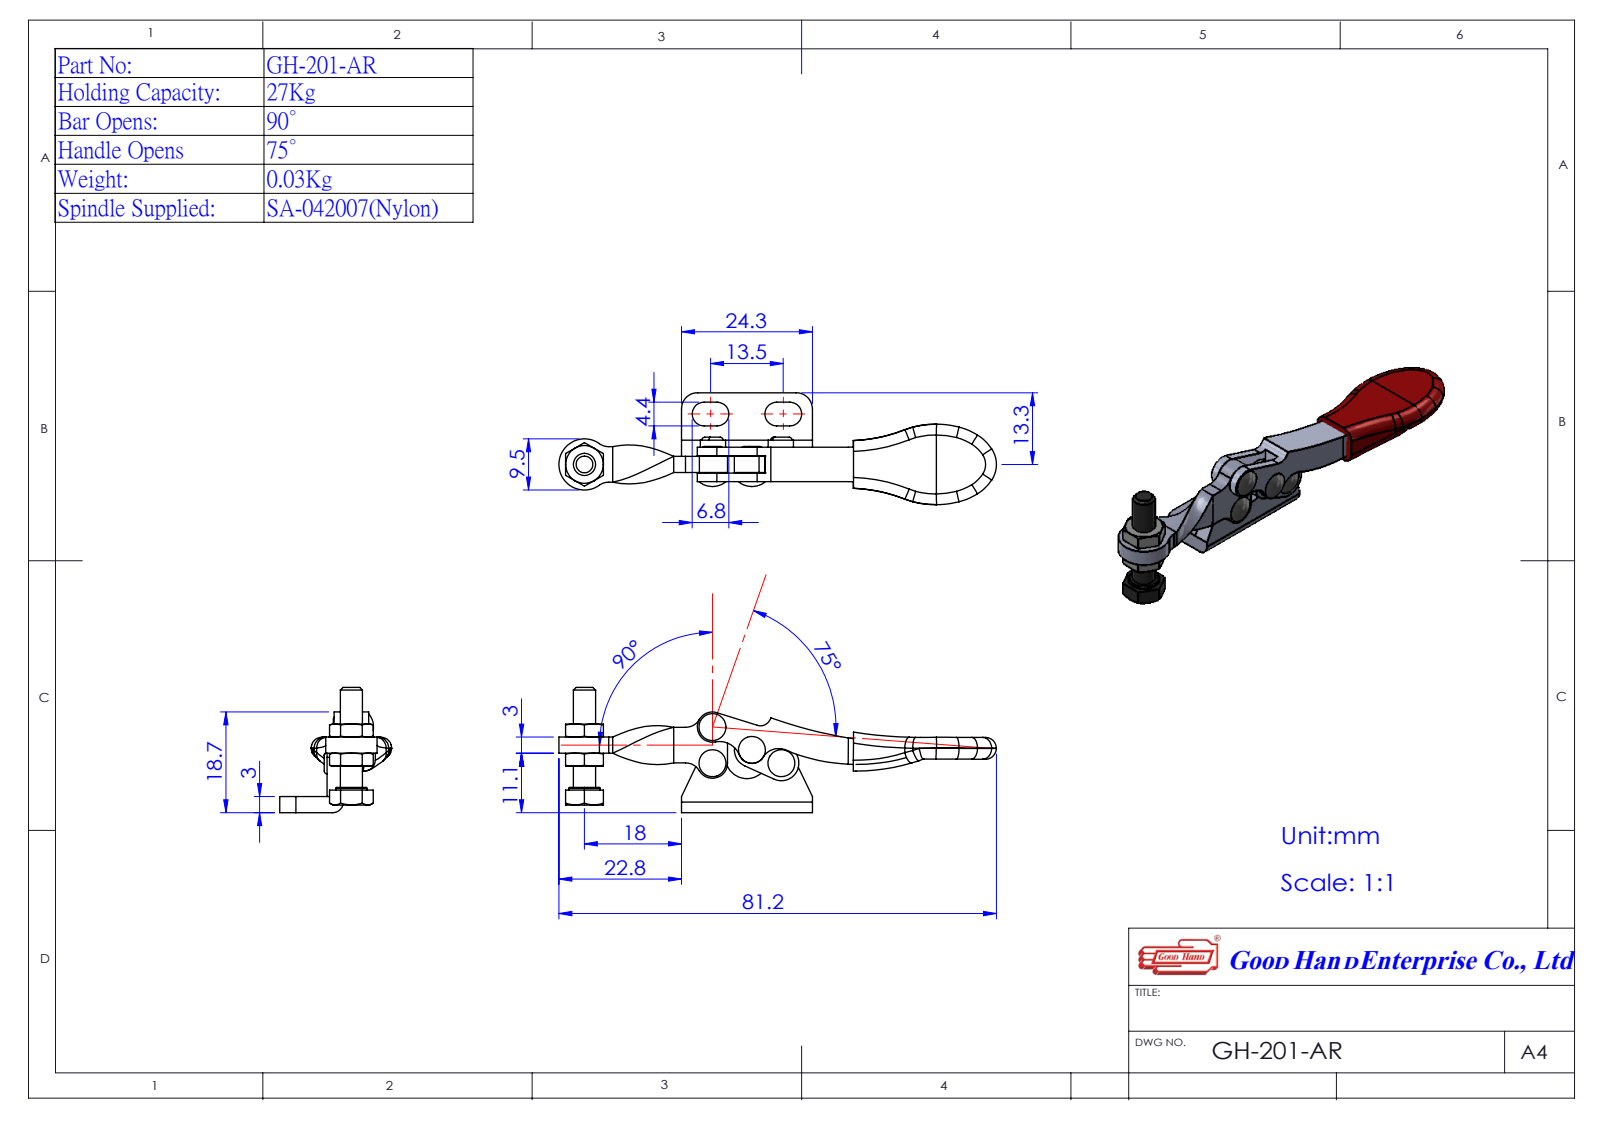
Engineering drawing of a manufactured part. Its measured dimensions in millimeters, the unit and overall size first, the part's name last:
Units: millimetres
Overall size (bounding box): 81.21 × 23.26 × 20.77
Round holes (diameter × count): ⌀2.3 ×4, ⌀3.3 ×1, ⌀4 ×1, ⌀4.3 ×1
Round bosses / shafts (diameter × count): ⌀5.8 ×1, ⌀4.1 ×1
Partial cylindrical surfaces — rounded edges, fillets, slot ends (radius × count): R3 ×6, R2.2 ×4, R11.01 ×4, R12.23 ×4, R2.5 ×2, R2.8 ×2, R3.25 ×2, R4 ×2
Main face-to-face distances: 3, 1.7, 1.6, 4.7, 11.05, 1.22, 2.82, 4.8, 3.1, 1.3
Hole centre spacings: 6, 6.7, 7.73, 8.47, 12.8, 14.45
Volume: 2 456 mm³ · Surface area: 5 774 mm²
Bodies: 6 solids, 291 faces (91 planar, 129 cylindrical, 71 other)
Part name (STEP PRODUCT): Group2^GH-201-AR(簡化); GH-201-AR(簡化); 鏡射1201AL13-1^GH-201-AR(簡化); Group5^GH-201-AR(簡化) (+2 more)
STEP written by: SolidWorks 2016 (AUTOMOTIVE_DESIGN)
